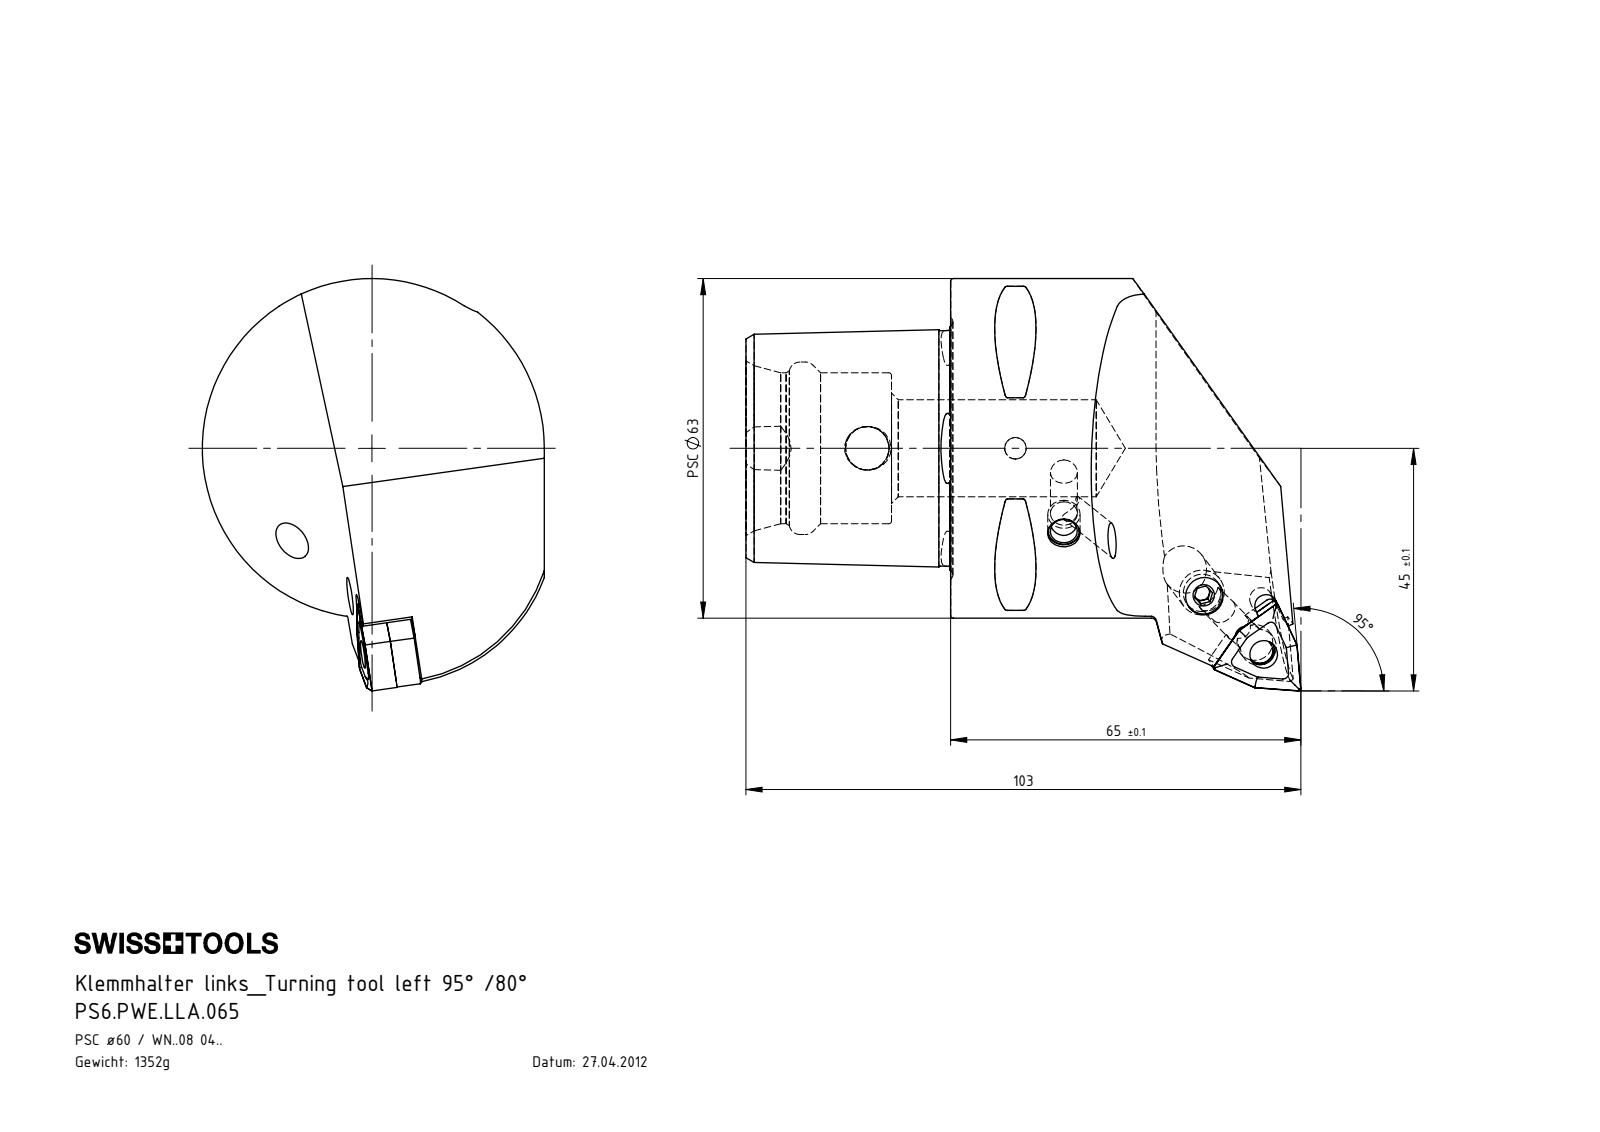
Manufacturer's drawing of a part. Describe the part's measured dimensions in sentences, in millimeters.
The part is named "PS6-PWE.LLA.065; KVT_MB_600_060; WNMG080404; WWE-ER2.101.004_A (+4 more)". Its 3-D file was written by "SolidWorks 2012 (CONFIG_CONTROL_DESIGN)". It is 8 solids with 349 faces: 100 planar, 82 cylindrical and 167 other. Overall it measures 103 by 76.5 by 63.5 millimeters. Its volume is 171 635 cubic millimeters and its surface area 31 379 square millimeters. Round holes: 2 of diameter 5, 2 of diameter 6.7, 1 of diameter 4, 1 of diameter 5.16, 1 of diameter 7, 1 of diameter 7.8, 1 of diameter 8.1, 1 of diameter 8.4, 1 of diameter 18, 1 of diameter 28, 1 of diameter 32. Round bosses or shafts: 1 of diameter 63, 1 of diameter 8, 1 of diameter 7.9, 1 of diameter 6.4, 1 of diameter 6, 1 of diameter 4.7, 1 of diameter 3.55. Partial cylindrical surfaces (rounded edges, fillets, slot ends): 8 of radius 0.5, 3 of radius 0.4, 3 of radius 1, 2 of radius 2.5, 2 of radius 6, 1 of radius 2, 1 of radius 2.1, 1 of radius 2.35. The main face-to-face distances are 38, 24.88, 4.76, 27, 11, 55.8, 4.75, 4.51, 37.8, 10.8. The hole center spacings are 15.6, 15.61, 27.5.
